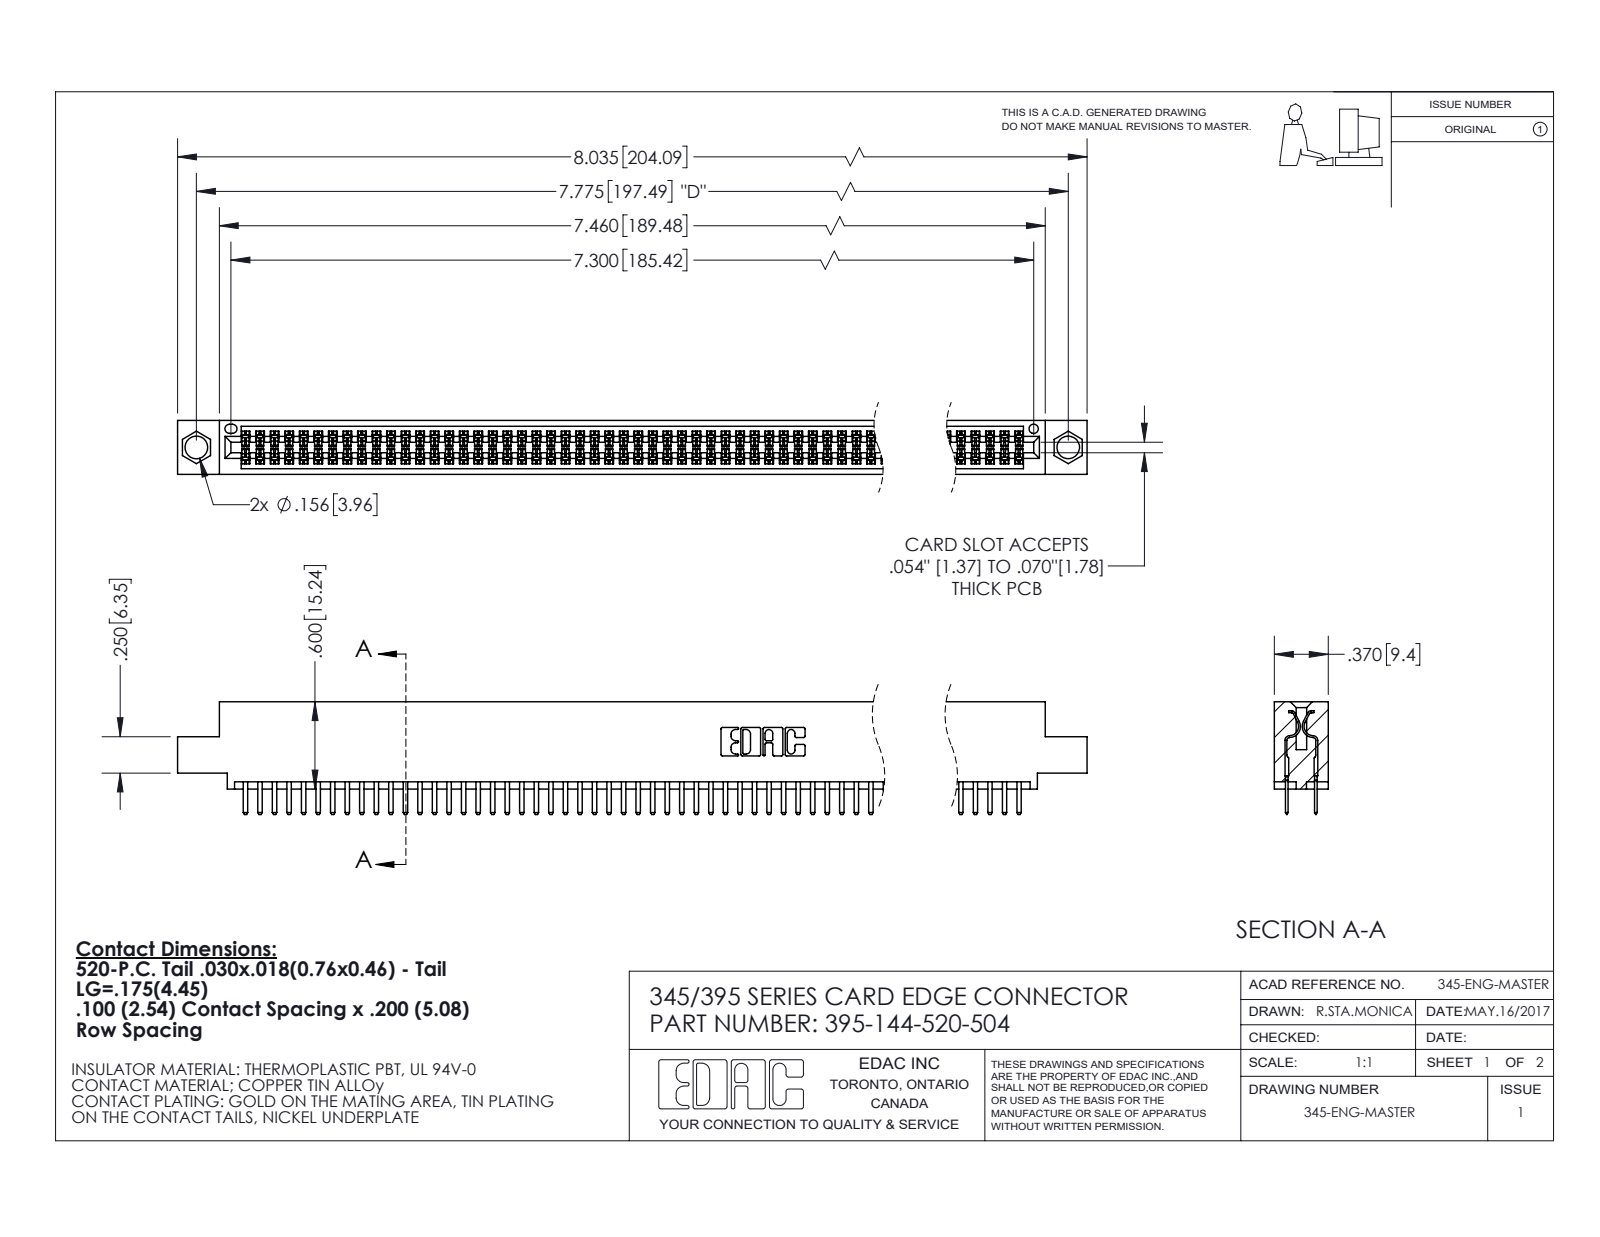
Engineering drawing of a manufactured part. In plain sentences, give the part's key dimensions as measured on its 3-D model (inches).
The part is named "395-144-520-504; 345-292-001_345-293-120; 345 Part_0.110 Offset - 0.156 Dia-TI". Its 3-D file was written by "SolidWorks 2020 (CONFIG_CONTROL_DESIGN)". It is 145 solids with 7920 faces: 5138 planar, 2782 cylindrical and 0 other. Overall it measures 8.035 by 0.775 by 0.37 inches. Its volume is 1.212 cubic inches and its surface area 46.11 square inches. Round holes: 2 of diameter 0.156, 1 of diameter 0.064. Partial cylindrical surfaces (rounded edges, fillets, slot ends): 217 of radius 0.006, 148 of radius 0.01, 22 of radius 0.01, 6 of radius 0.007, 6 of radius 0.031, 3 of radius 0.026, 2 of radius 0.014, 2 of radius 0.019. The main face-to-face distances are 0.072, 0.298, 0.2, 0.37, 0.098, 0.272, 0.025, 0.225, 0.022, 0.072. The hole center spacings are 0.27, 7.539, 7.775.
